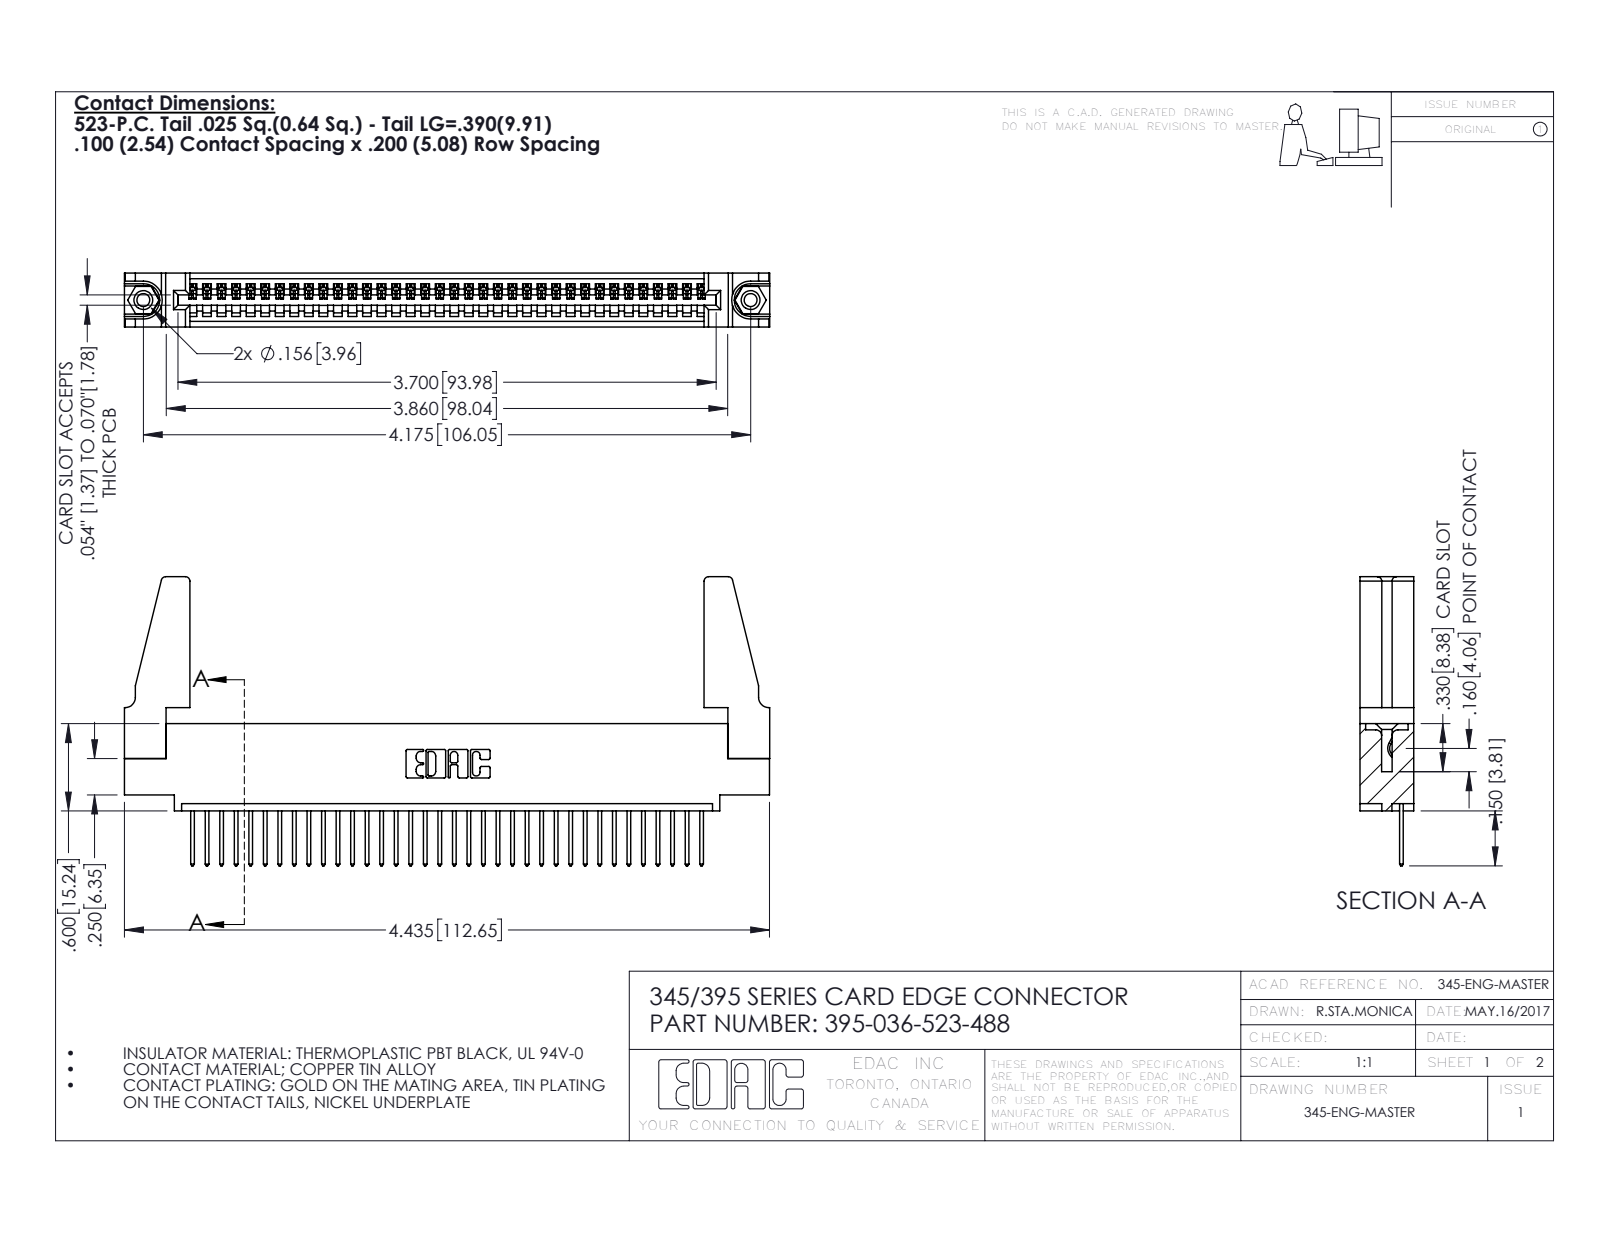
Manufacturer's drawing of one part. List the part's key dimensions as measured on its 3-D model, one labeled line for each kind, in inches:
Part name (STEP PRODUCT): 345 Part_0.110 Offset - 0.156 Dia-TH; 345-220-078_345-220-088; 345-292-001_345-293-123; 395-036-523-488 (+1 more)
STEP written by: SolidWorks 2016 (CONFIG_CONTROL_DESIGN)
Units: inches
Bodies: 41 solids, 2342 faces (1596 planar, 730 cylindrical, 16 other)
Overall size (bounding box): 4.436 × 1.987 × 0.37
Volume: 0.843 in³ · Surface area: 26.67 in²
Round holes (diameter × count): ⌀0.089 ×2, ⌀0.125 ×2, ⌀0.156 ×2, ⌀0.064 ×1
Round bosses / shafts (diameter × count): ⌀0.155 ×2
Partial cylindrical surfaces — rounded edges, fillets, slot ends (radius × count): R0.006 ×72, R0.01 ×72, R0.01 ×22, R0.03 ×8, R0.007 ×6, R0.031 ×6, R0.026 ×3, R0.031 ×2
Main face-to-face distances: 0.072, 0.298, 0.37, 0.098, 0.272, 0.025, 0.2, 0.225, 0.149, 0.072
Hole centre spacings: 0.27, 3.939, 4.175
